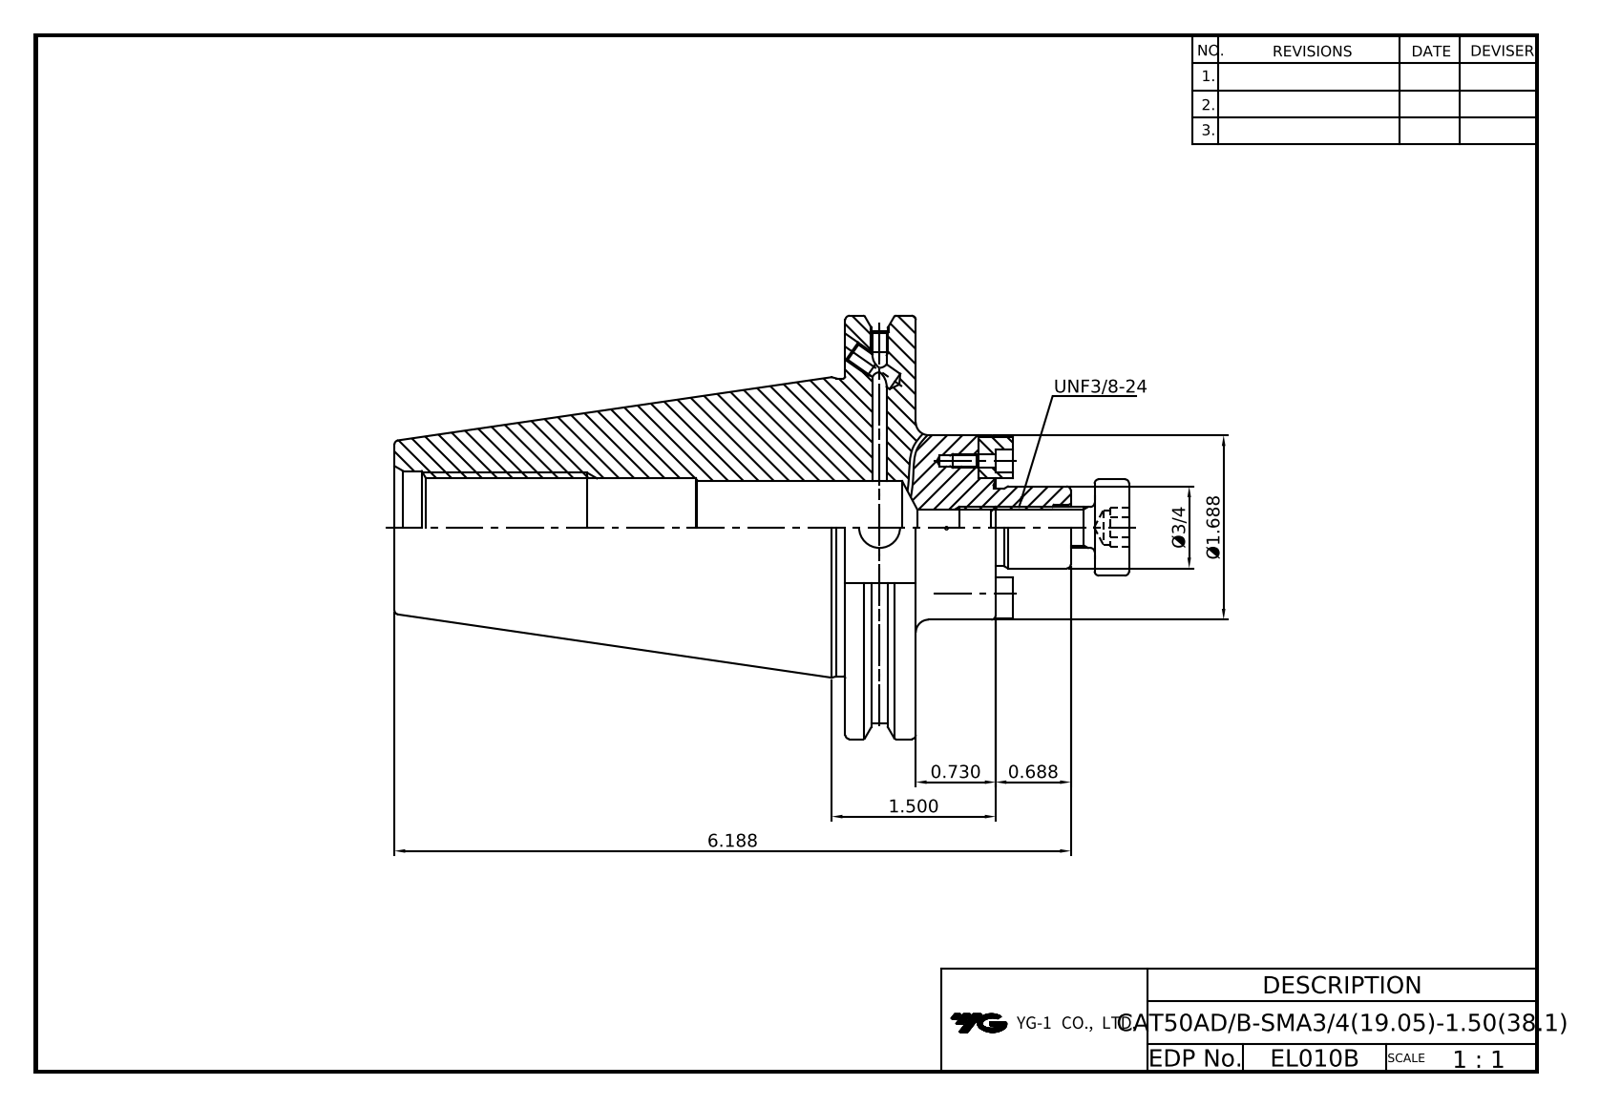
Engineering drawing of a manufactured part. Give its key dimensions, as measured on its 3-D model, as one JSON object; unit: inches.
{"part_name": "LO-CAT50ADB-SMA19.05-38.1; DRIVE KEY-7.93x7.93x9.5; HEX'' WRENCH BOLT-UNC#5-40x5_16L; COLLAR BOLT-UNF3_8-24x24L", "step_written_by": "Autodesk Inventor 2025 (AP242_MANAGED_MODEL_BASED_3D_ENGINEERING_MIM_LF)", "units": "inches", "bodies": {"solids": 6, "faces": 165, "planar": 88, "cylindrical": 43, "other": 34}, "overall_size": [6.897, 3.875, 3.728], "volume_in3": 21.92, "surface_area_in2": 82.03, "round_holes": [[0.098, 2], [0.128, 2], [0.13, 2], [0.163, 2], [0.165, 2], [0.197, 2], [0.213, 2], [0.313, 1], [0.33, 1], [0.375, 1], [0.413, 1], [0.865, 1]], "round_bosses_or_shafts": [[0.205, 2], [0.125, 2], [3.875, 1], [3.594, 1], [2.726, 1], [1.688, 1], [0.882, 1], [0.75, 1]], "partial_cylinders_radius": [[0.156, 2]], "face_to_face_distances": [0.625, 1.375, 0.75, 4.125, 4.75, 5.5, 2.875, 1.02, 6.897, 2.772], "hole_center_spacings": [0.609, 1.217]}
